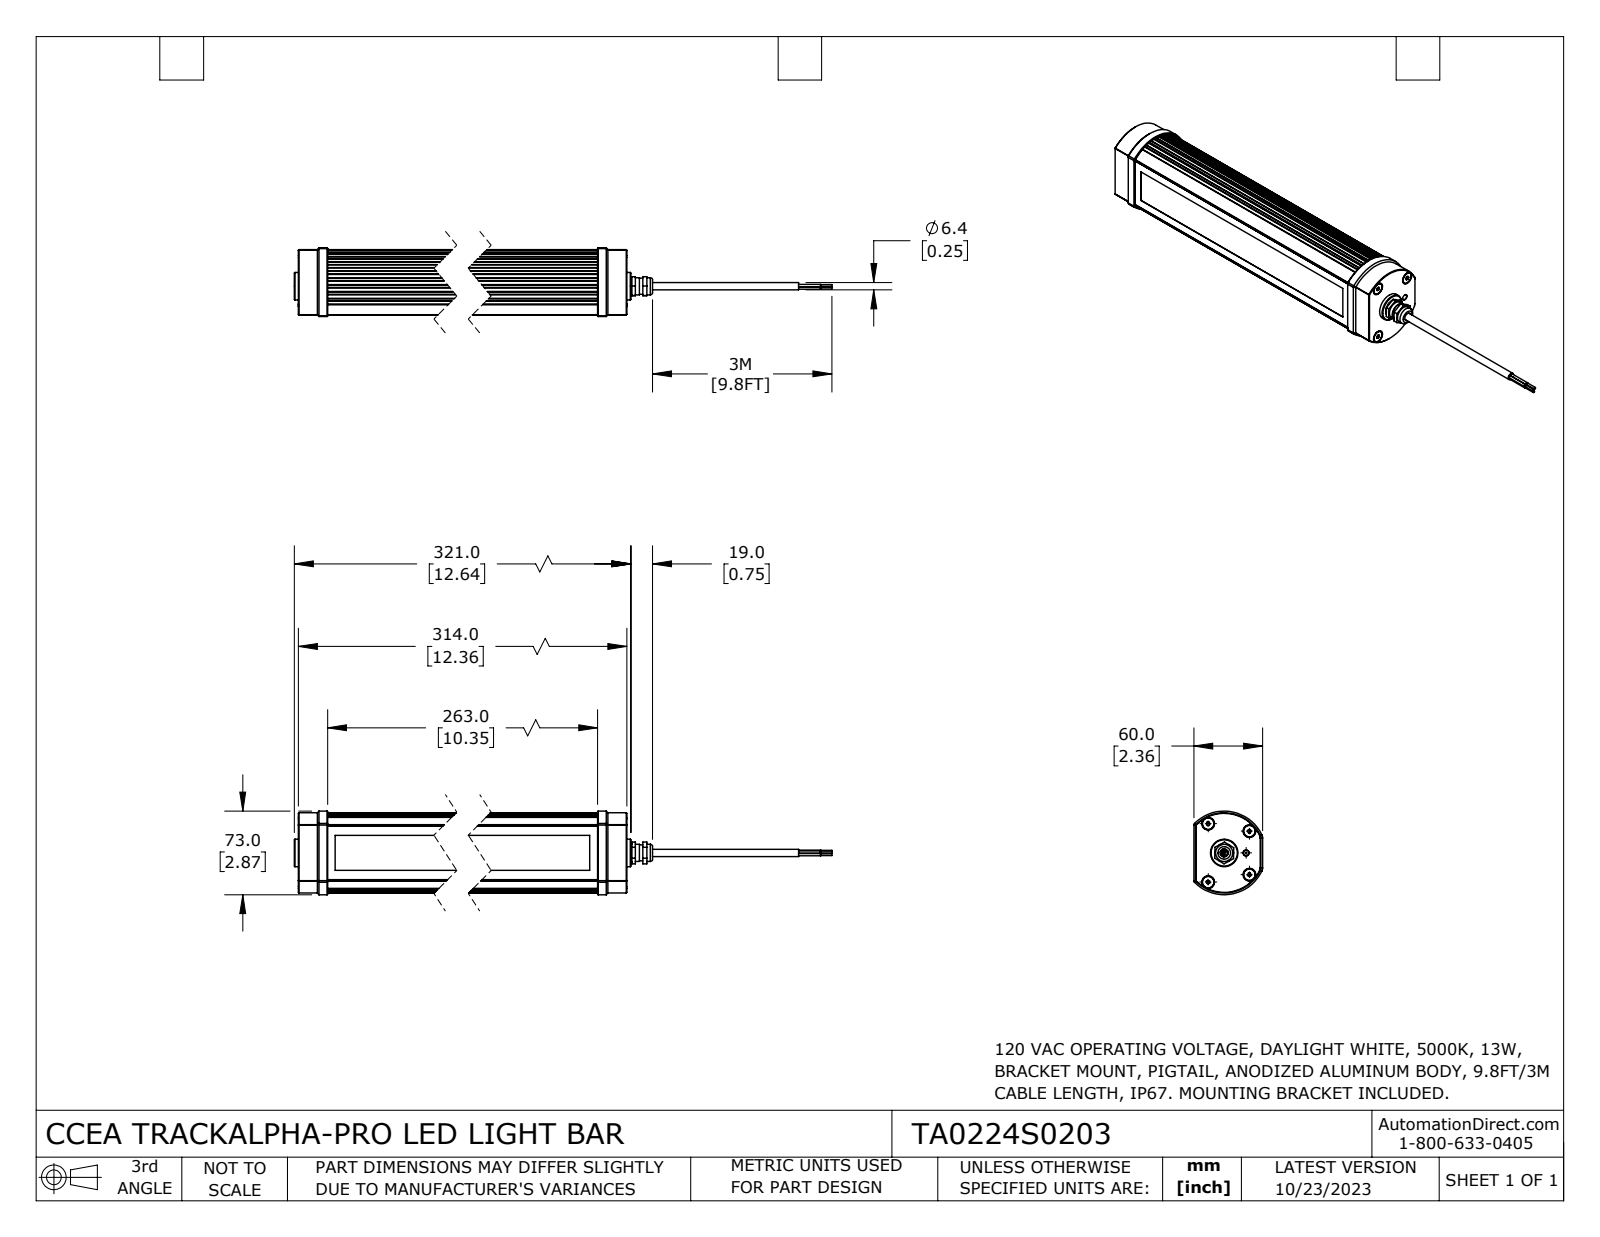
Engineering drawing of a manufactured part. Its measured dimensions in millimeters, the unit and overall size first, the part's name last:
Units: millimetres
Overall size (bounding box): 496.5 × 73 × 60
Round holes (diameter × count): ⌀5.5 ×4, ⌀1.1 ×3, ⌀3 ×2, ⌀10 ×2, ⌀4.9 ×1, ⌀7 ×1, ⌀14 ×1, ⌀27 ×1
Round bosses / shafts (diameter × count): ⌀10 ×4, ⌀5 ×4, ⌀1.7 ×3, ⌀1.6 ×3, ⌀1 ×3, ⌀2.1 ×2, ⌀24 ×1, ⌀15 ×1
Partial cylindrical surfaces — rounded edges, fillets, slot ends (radius × count): R0.5 ×22, R0.3 ×16, R1.5 ×10, R1.9 ×8, R2 ×4, R5 ×3, R1 ×2, R5.5 ×2
Main face-to-face distances: 5, 0.5, 5.5, 51.4, 51.9, 56.9, 56.9, 5.6, 5.1, 20.5
Hole centre spacings: 8.5, 12.8, 18.4, 19.2, 21.1, 24.1, 25.2, 29.1
Volume: 1 049 000 mm³ · Surface area: 157 900 mm²
Bodies: 19 solids, 625 faces (196 planar, 279 cylindrical, 150 other)
Part name (STEP PRODUCT): TA0224S0203
STEP written by: SolidWorks 2023 (CONFIG_CONTROL_DESIGN)
